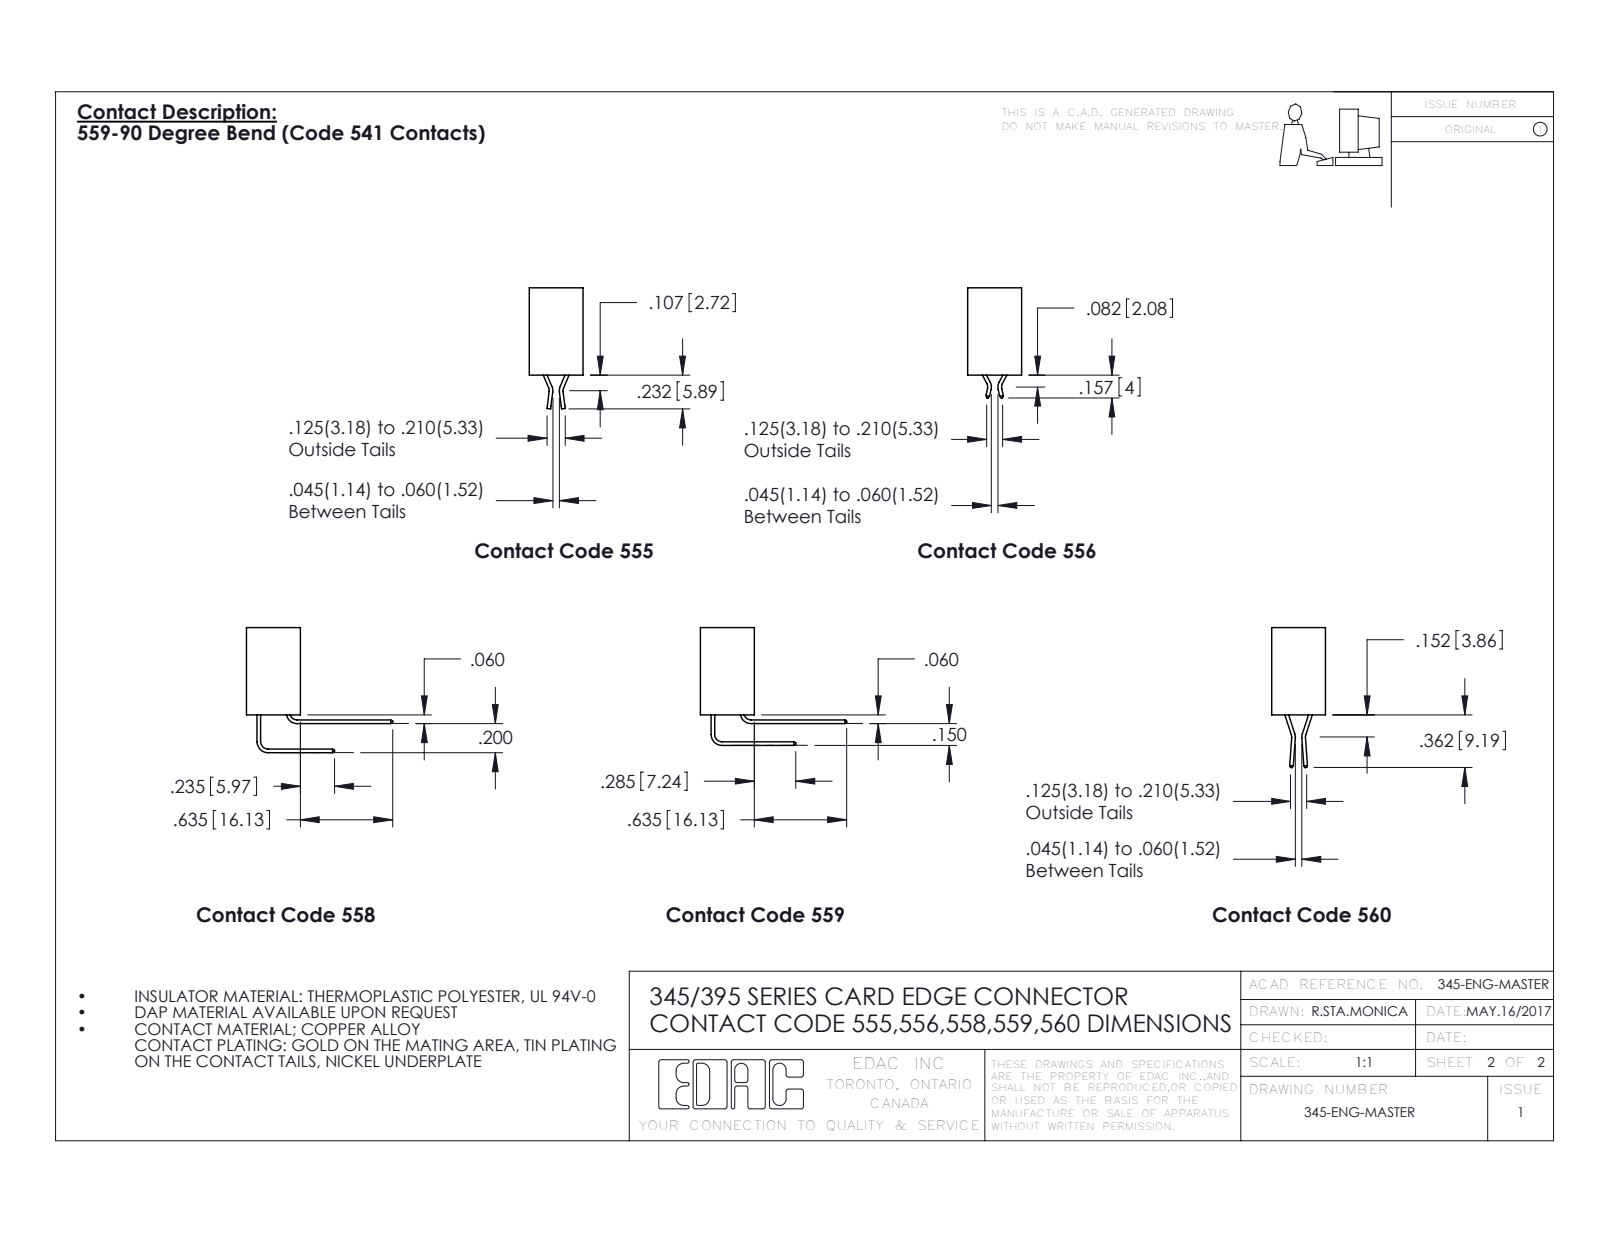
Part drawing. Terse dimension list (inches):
name: 395-069-559-612; 345 Part_0.170 Offset - Side Mount; 345-292-001_558 559 Tail - 1
written by: SolidWorks 2016 (CONFIG_CONTROL_DESIGN)
unit: in
bodies: 70 solids, 4270 faces (2982 planar, 1288 cylindrical, 0 other)
size: 7.735 × 1.005 × 0.659
volume: 1.154 in³; area: 41.59 in²
holes: 2× ⌀0.128, 1× ⌀0.064
rounds: 138× R0.006, 22× R0.01, 6× R0.007, 6× R0.031, 3× R0.026, 2× R0.031, 2× R0.04, 1× R0.014
face distances: 0.072, 0.298, 0.37, 0.2, 0.098, 0.272, 0.025, 0.225, 0.175, 0.149
hole spacings: 7.475
